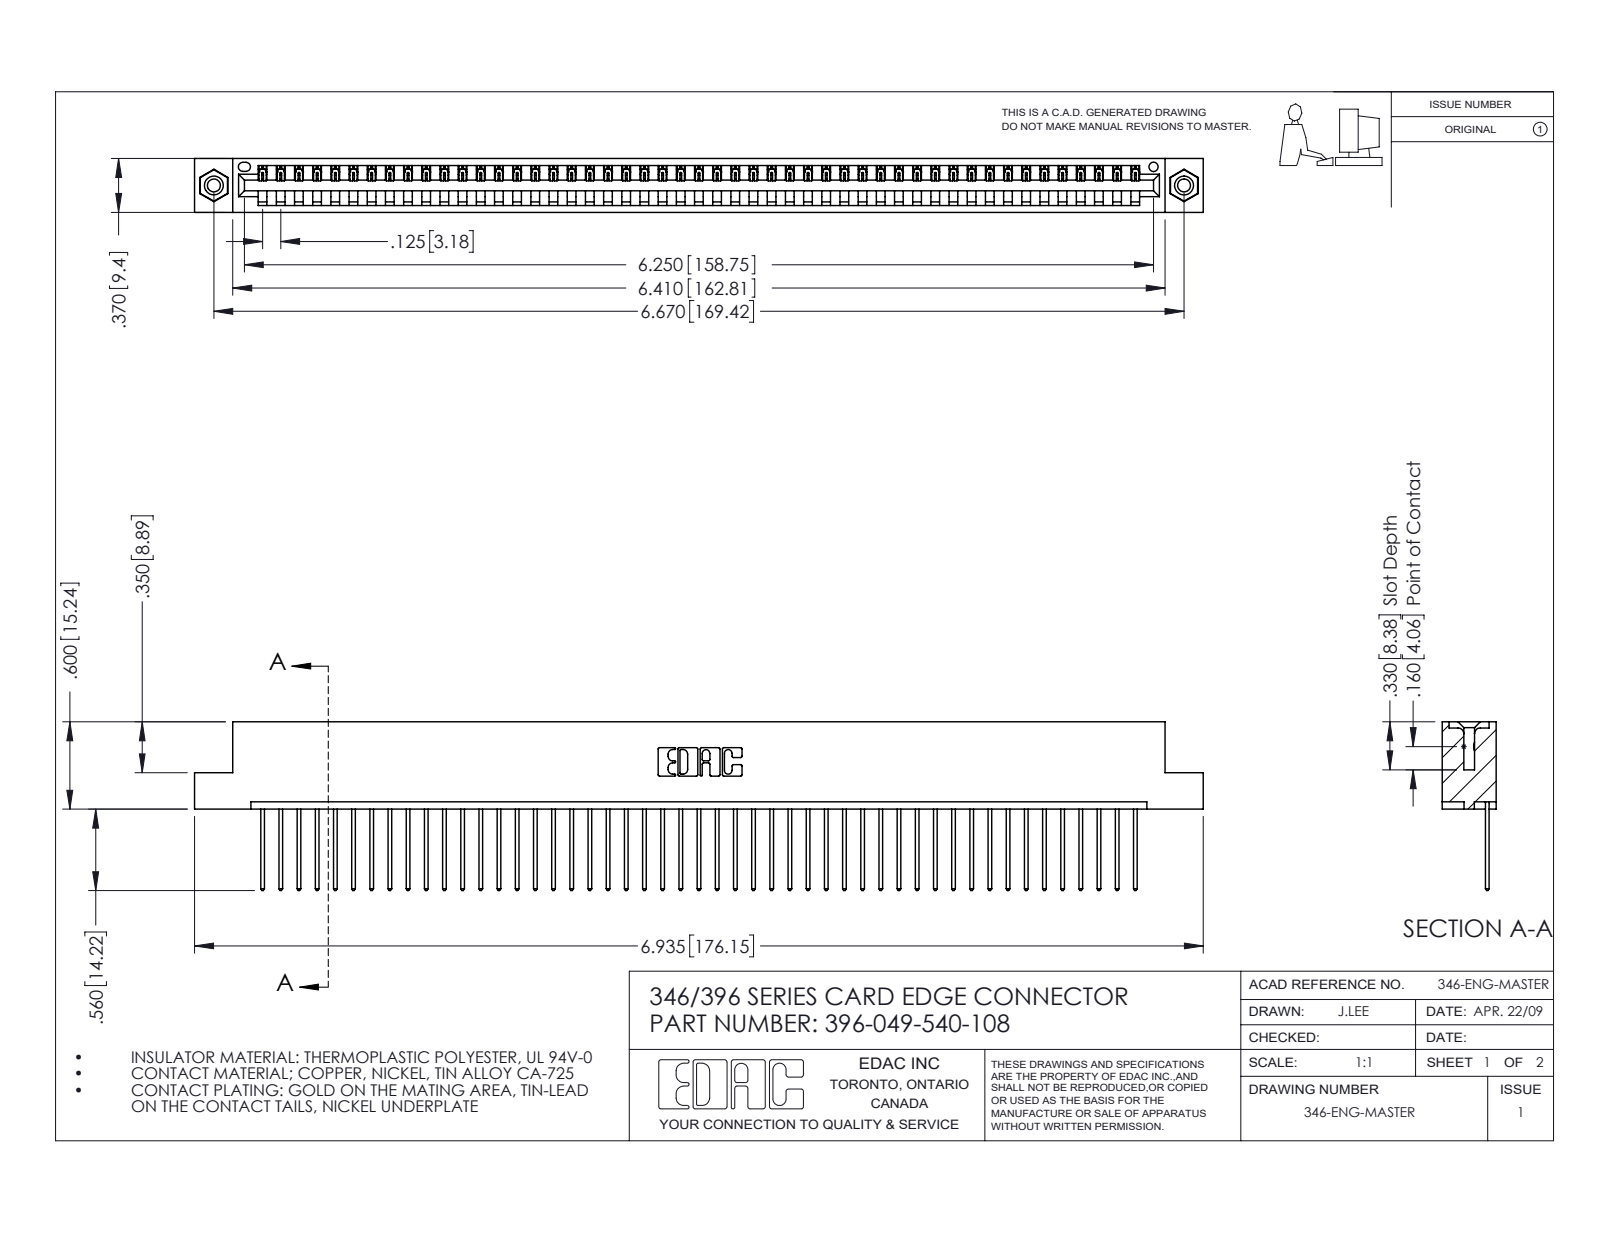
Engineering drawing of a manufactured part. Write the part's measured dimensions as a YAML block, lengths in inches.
part_name: "346 Part_Flush Mounting Lugs - 0.156 Dia-TI; 396-049-540-108; 345-292-001_345-293-140; 345-250-001_345-250-003-102"
step_written_by: "SolidWorks 2016 (CONFIG_CONTROL_DESIGN)"
units: inches
bodies: {solids: 52, faces: 3024, planar: 2068, cylindrical: 940, other: 16}
overall_size: [6.935, 1.16, 0.37]
volume: 1.036
surface_area: 33.78
round_holes:
  - {diameter: 0.089, count: 2}
  - {diameter: 0.125, count: 2}
  - {diameter: 0.156, count: 2}
  - {diameter: 0.064, count: 1}
round_bosses_or_shafts:
  - {diameter: 0.155, count: 2}
partial_cylinders:
  - {radius: 0.006, count: 98}
  - {radius: 0.01, count: 98}
  - {radius: 0.01, count: 22}
  - {radius: 0.007, count: 6}
  - {radius: 0.031, count: 6}
  - {radius: 0.026, count: 3}
  - {radius: 0.031, count: 2}
  - {radius: 0.04, count: 2}
face_to_face_distances: [0.048, 0.322, 0.37, 0.25, 0.072, 0.298, 0.025, 0.148, 0.222, 0.1]
hole_center_spacings: [0.246, 6.461, 6.67]
